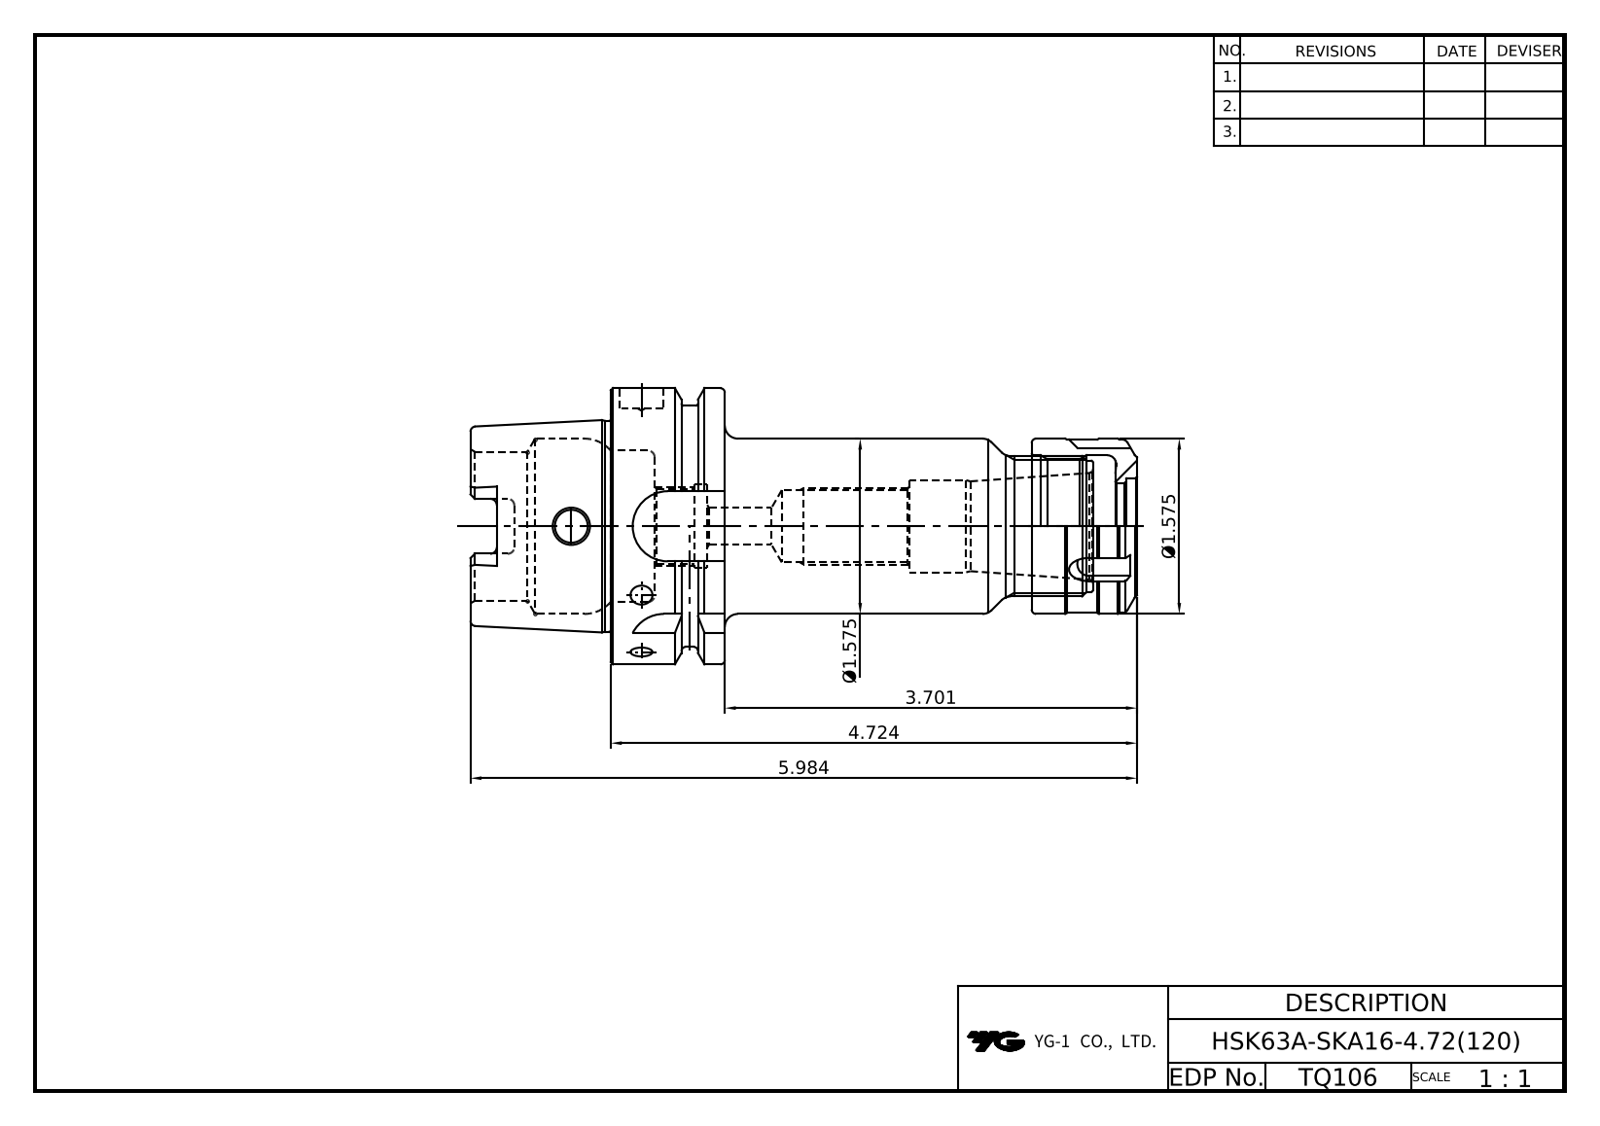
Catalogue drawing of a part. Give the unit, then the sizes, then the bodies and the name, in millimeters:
Units: millimetres
Overall size (bounding box): 152 × 63 × 63
Round holes (diameter × count): ⌀7.5 ×1, ⌀8 ×1, ⌀10 ×1, ⌀15.75 ×1, ⌀16.92 ×1, ⌀19 ×1, ⌀19.8 ×1, ⌀21 ×1, ⌀22 ×1, ⌀32 ×1, ⌀32.4 ×1, ⌀34 ×1
Round bosses / shafts (diameter × count): ⌀63 ×1, ⌀55 ×1, ⌀48.04 ×1, ⌀40 ×1, ⌀39.6 ×1, ⌀30 ×1
Partial cylindrical surfaces — rounded edges, fillets, slot ends (radius × count): R1.5 ×6, R2.88 ×4, R8 ×4
Main face-to-face distances: 26, 10, 42, 16, 110, 58, 115.1, 105.1, 89.1, 94
Volume: 166 110 mm³ · Surface area: 43 296 mm²
Bodies: 2 solids, 193 faces (63 planar, 54 cylindrical, 76 other)
Part name (STEP PRODUCT): LO-HSK63A-SKA16-120; SKN16-NUT
STEP written by: Autodesk Inventor 2024 (AUTOMOTIVE_DESIGN)
